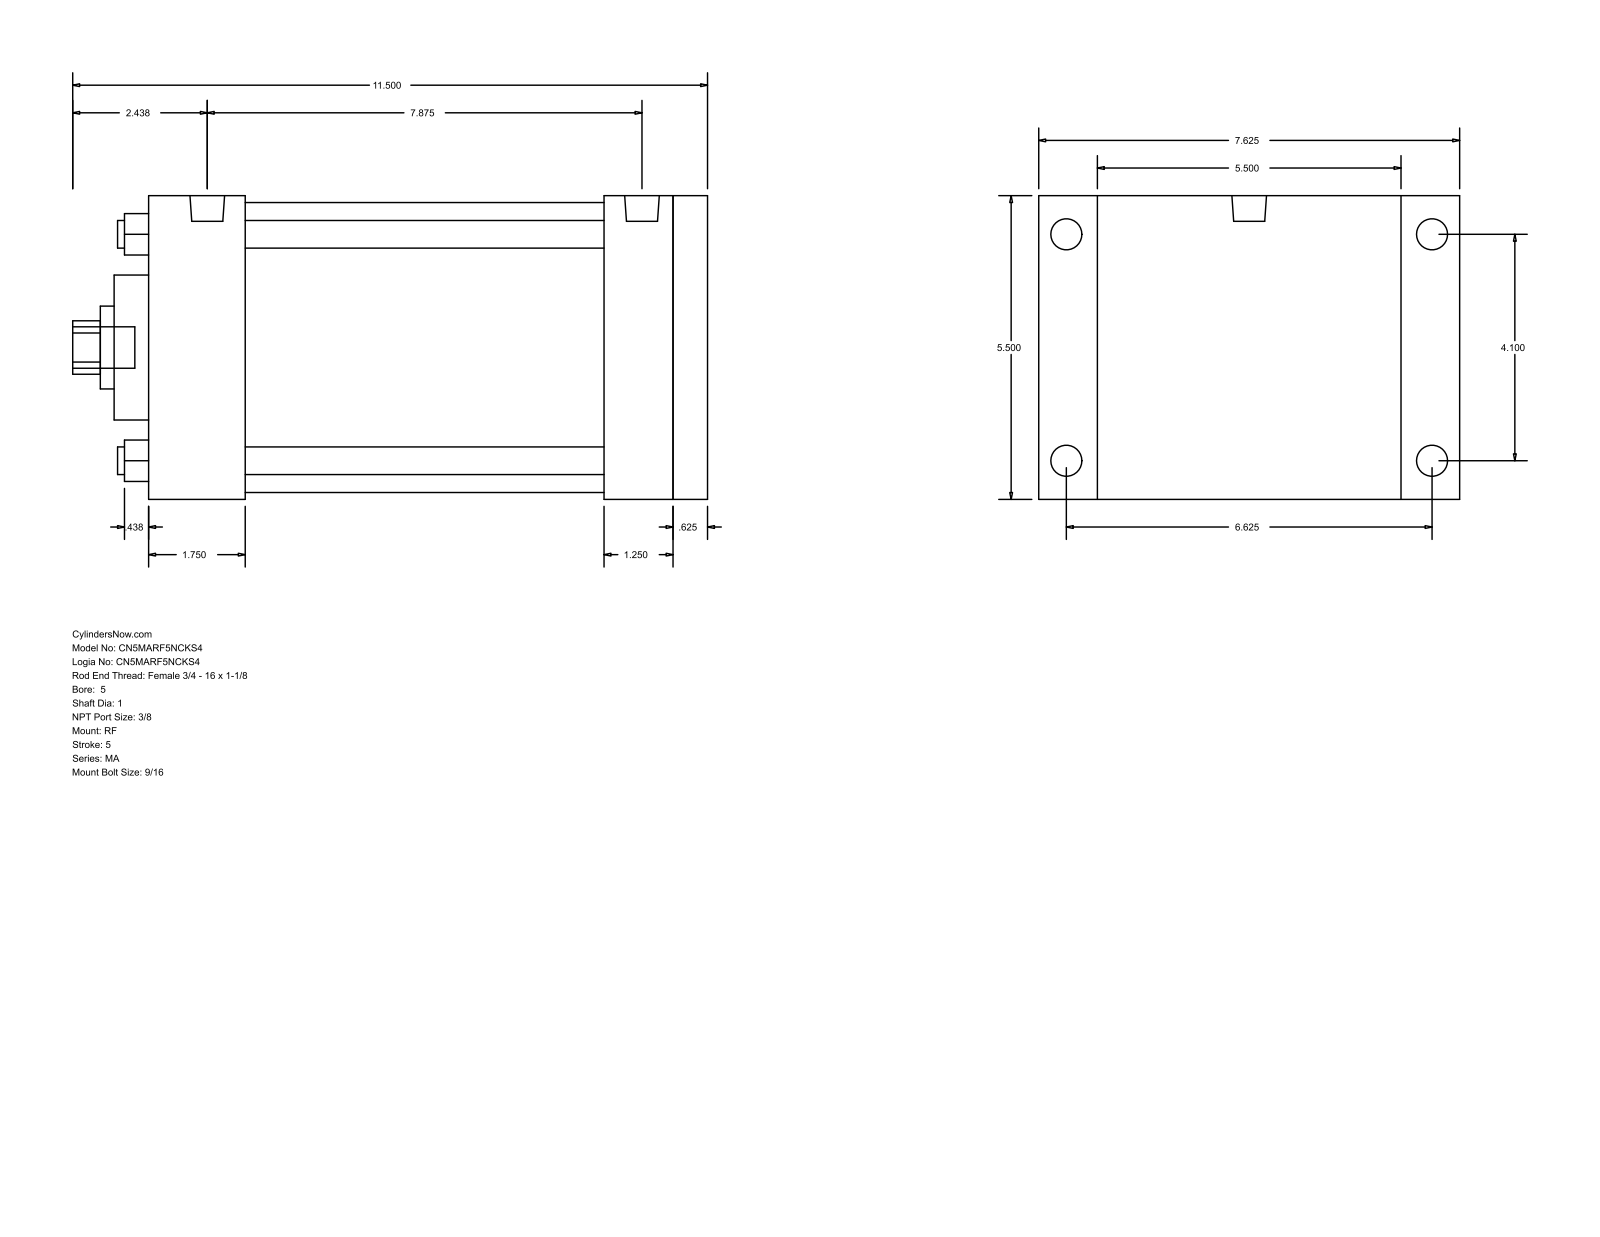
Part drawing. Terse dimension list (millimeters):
name: MA_RF__0500_1
written by: GSSL Pune (CONFIG_CONTROL_DESIGN)
unit: mm
bodies: 0 solids, 94 faces (65 planar, 29 cylindrical, 0 other)
size: 292.1 × 193.68 × 139.7
holes: 4× ⌀12.7, 1× ⌀25.4, 1× ⌀38.1, 1× ⌀66.67, 1× ⌀133.35
bosses: 4× ⌀14.29, 4× ⌀11.11, 2× ⌀15.93, 1× ⌀19.05
rounds: 1× R12.29
face distances: 139.7, 257.18, 15.87, 241.31, 44.46, 196.85, 212.72, 209.55, 165.09, 31.76
hole spacings: 73.64, 104.14, 147.28
